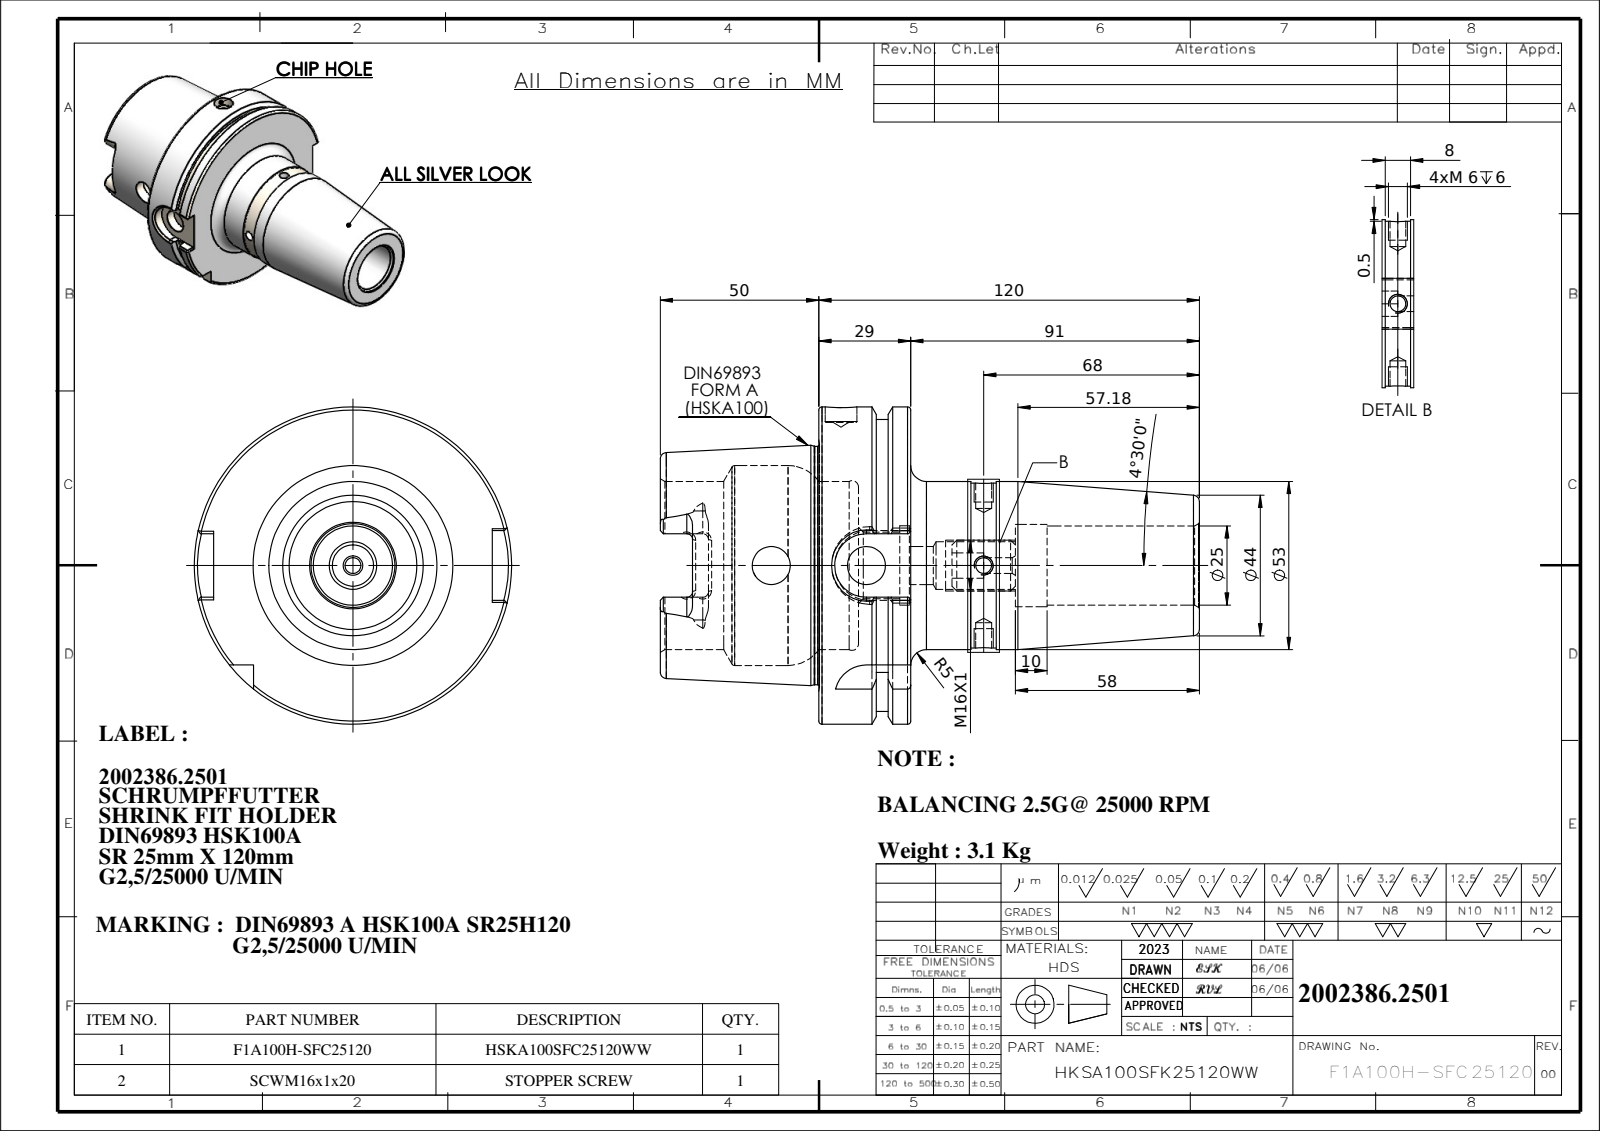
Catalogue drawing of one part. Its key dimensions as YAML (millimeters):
part_name: "91100A-SR25120; HSKA100SFC25120WW; SCWM16X1P"
step_written_by: "SolidWorks 2018 (CONFIG_CONTROL_DESIGN)"
units: millimeters
bodies: {solids: 2, faces: 219, planar: 61, cylindrical: 70, other: 88}
overall_size: [169.95, 100, 100]
volume: 402663
surface_area: 71307
round_holes:
  - {diameter: 5, count: 3}
  - {diameter: 12, count: 3}
  - {diameter: 10, count: 1}
  - {diameter: 15, count: 1}
  - {diameter: 21, count: 1}
  - {diameter: 24.99, count: 1}
  - {diameter: 25, count: 1}
  - {diameter: 25.99, count: 1}
  - {diameter: 53, count: 1}
  - {diameter: 63, count: 1}
round_bosses_or_shafts:
  - {diameter: 100, count: 1}
  - {diameter: 92, count: 1}
  - {diameter: 75.16, count: 1}
  - {diameter: 52, count: 1}
  - {diameter: 16, count: 1}
partial_cylinders:
  - {radius: 1.8, count: 6}
  - {radius: 4.88, count: 4}
  - {radius: 10, count: 2}
  - {radius: 11, count: 1}
face_to_face_distances: [28.95, 16.45, 12.5, 50, 62.5, 78.95, 169.95, 119.95, 107.45, 91]
hole_center_spacings: [30, 36.95, 44.95, 66.95]
